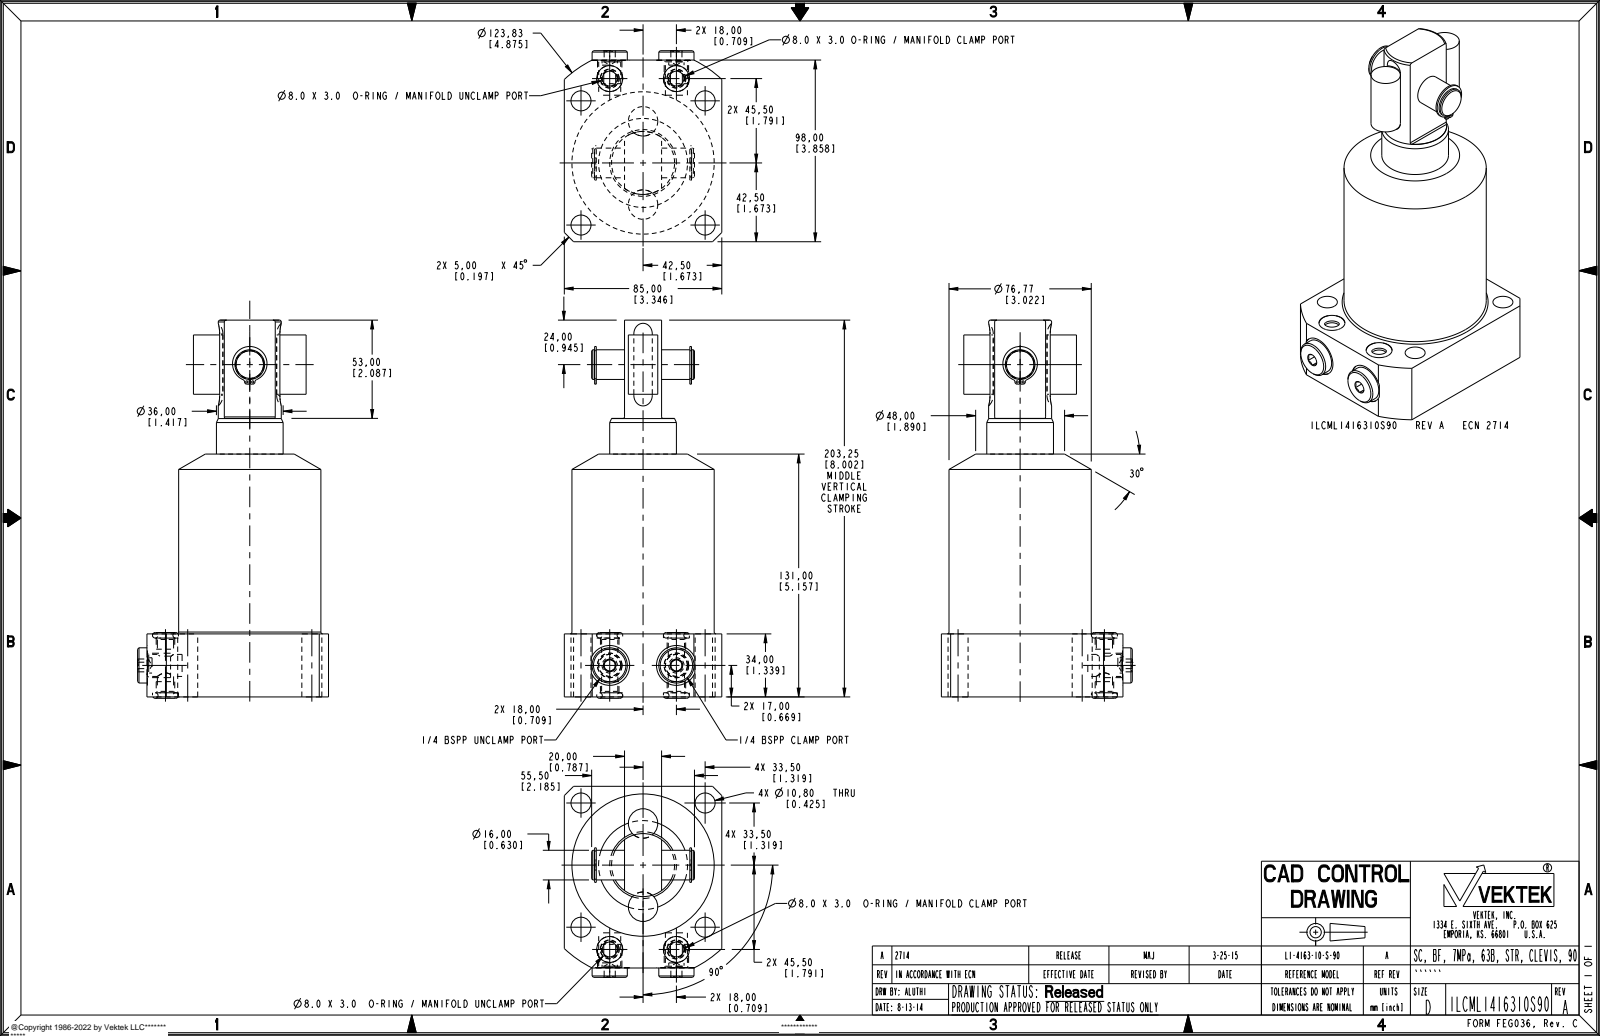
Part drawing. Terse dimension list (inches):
name: ILCML1416310S90
written by: PRO/ENGINEER BY PARAMETRIC TECHNOLOGY CORPORATION, 2013320 (AUTOMOTIVE_DESIGN)
unit: in
bodies: 7 solids, 246 faces (84 planar, 98 cylindrical, 64 other)
size: 8.031 × 4.057 × 3.346
volume: 46.94 in³; area: 115.3 in²
holes: 4× ⌀0.425, 2× ⌀0.047, 2× ⌀0.344, 2× ⌀0.468, 2× ⌀0.551, 2× ⌀0.846, 1× ⌀0.61
bosses: 2× ⌀0.748, 2× ⌀0.625, 2× ⌀0.518, 2× ⌀0.394, 2× ⌀0.325, 1× ⌀3.022, 1× ⌀1.417, 1× ⌀1.339
rounds: 2× R0.031, 2× R0.047, 2× R0.053, 2× R0.313, 1× R2.437
face distances: 3.346, 1.339, 2.067, 1.28, 0.787, 3.858, 5.157, 3.819, 8.002, 6.663
hole spacings: 2.638, 0.374, 0.772, 1.417, 2.082, 3.17, 3.713, 3.73
